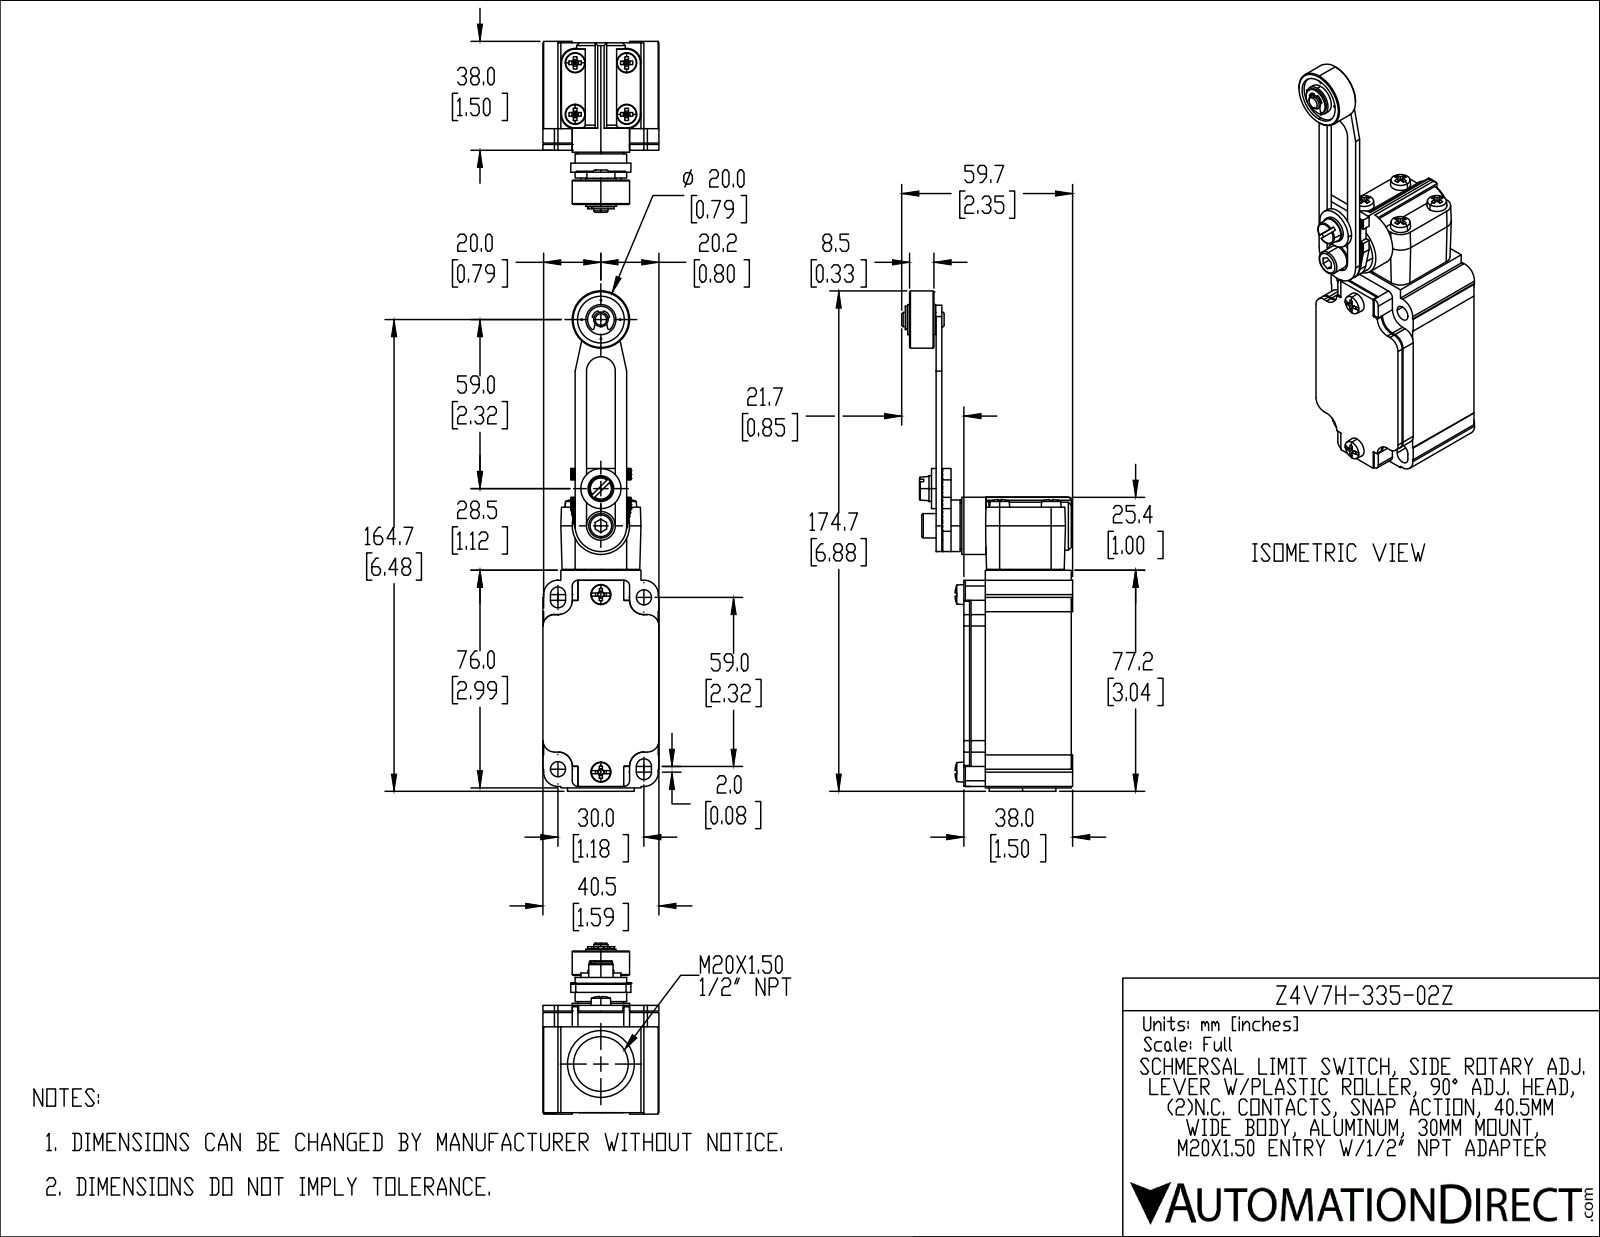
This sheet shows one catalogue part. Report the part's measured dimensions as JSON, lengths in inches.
{"part_name": "Z4V7H-335-02Z", "step_written_by": "SolidWorks 2019 (AUTOMOTIVE_DESIGN)", "units": "inches", "bodies": {"solids": 1, "faces": 819, "planar": 592, "cylindrical": 160, "other": 67}, "overall_size": [6.878, 2.35, 1.594], "volume_in3": 7.899, "surface_area_in2": 49.7, "round_holes": [[0.02, 4], [0.209, 2], [0.642, 1], [0.65, 1], [0.75, 1]], "round_bosses_or_shafts": [[0.787, 2], [0.709, 2], [0.157, 2], [0.079, 2], [0.917, 1], [0.669, 1], [0.63, 1], [0.551, 1]], "partial_cylinders_radius": [[0.197, 13], [0.01, 12], [0.157, 12], [0.012, 4], [0.079, 4], [0.104, 4], [0.128, 4], [0.197, 4]], "face_to_face_distances": [0.079, 0.02, 1.398, 1.378, 1.476, 0.098, 0.382, 0.461, 0.48, 1.858], "hole_center_spacings": [0.266, 0.376, 0.531, 2.847, 1.148, 2.569, 2.641, 2.835]}
